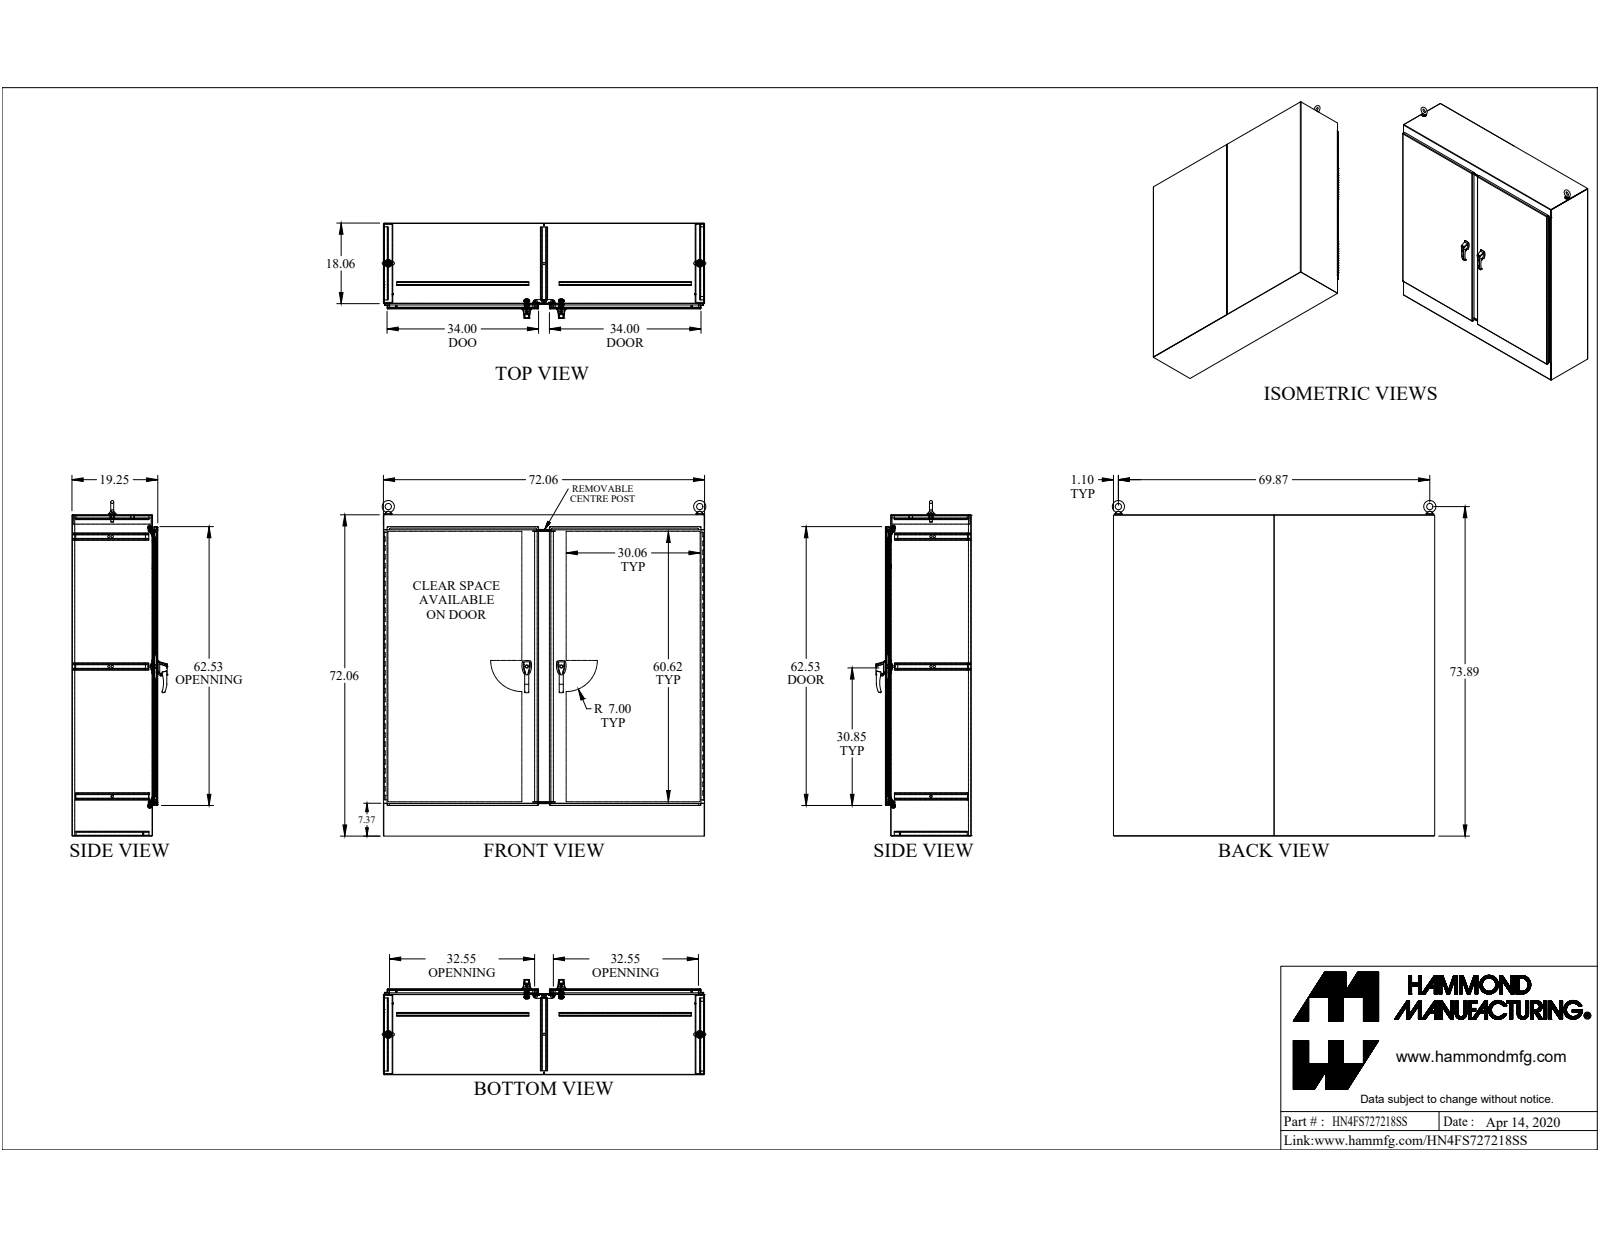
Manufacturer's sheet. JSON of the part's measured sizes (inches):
{"part_name": "HN4FS727218SS", "step_written_by": "SolidWorks 2019 (CONFIG_CONTROL_DESIGN)", "units": "inches", "bodies": {"solids": 106, "faces": 2965, "planar": 1563, "cylindrical": 1156, "other": 246}, "overall_size": [75.256, 72.604, 21.362], "volume_in3": 1776, "surface_area_in2": 37531, "round_holes": [[0.304, 20], [0.35, 8], [0.25, 7], [0.5, 7], [0.257, 4], [0.28, 4], [0.281, 4], [0.313, 4], [0.39, 4], [0.413, 4], [0.201, 3], [0.313, 3]], "round_bosses_or_shafts": [[1, 4], [0.75, 4], [0.63, 4], [0.625, 4], [0.44, 4], [0.37, 4], [0.313, 4], [0.281, 4]], "partial_cylinders_radius": [[0.043, 54], [0.138, 48], [0.5, 33], [0.1, 28], [0.125, 27], [0.06, 24], [0.318, 19], [0.017, 16]], "face_to_face_distances": [0.095, 19.152, 71.965, 19.057, 19.247, 71.87, 72.06, 1.187, 17.965, 1.282], "hole_center_spacings": [6, 70.584, 12, 71.345, 18, 72.595, 24, 74.311]}
